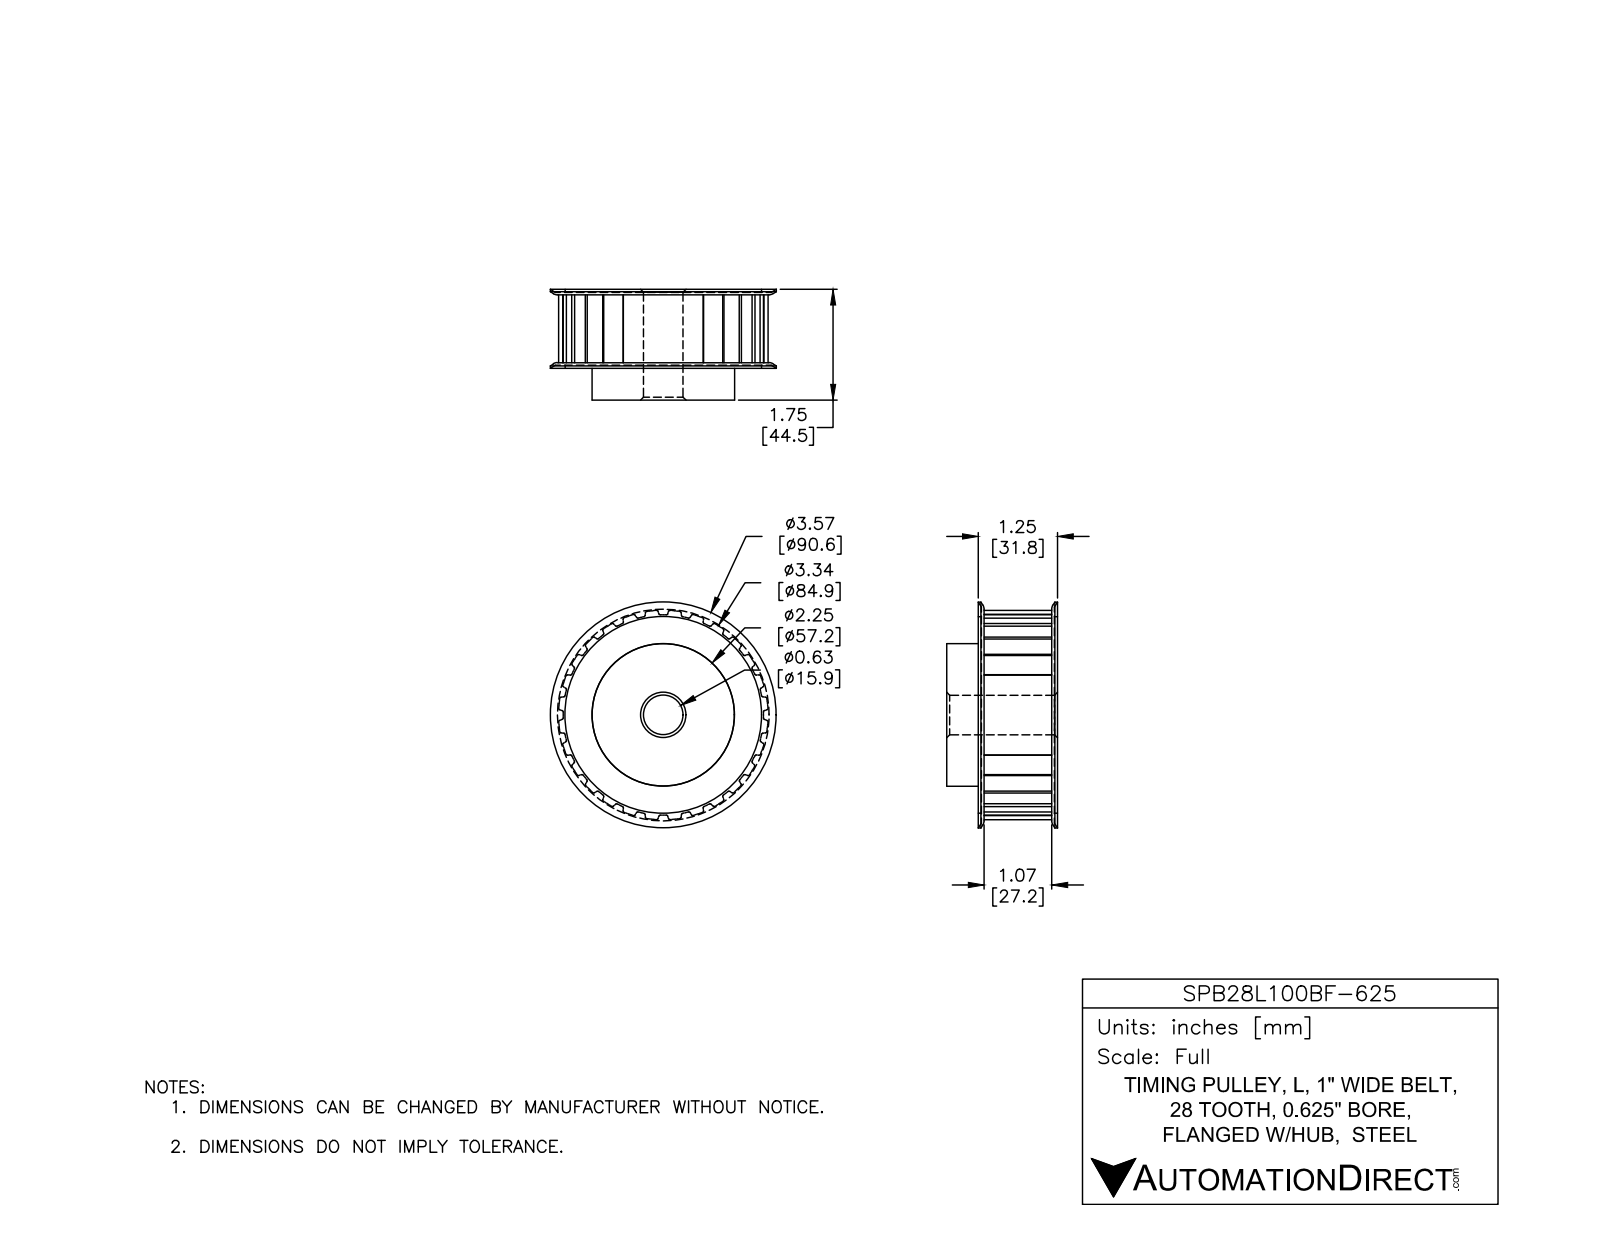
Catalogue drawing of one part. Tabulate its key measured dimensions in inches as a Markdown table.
| quantity | value |
| --- | --- |
| part name | SPB28L100BF-625 |
| STEP written by | SolidWorks 2015 (AUTOMOTIVE_DESIGN) |
| units | inches |
| bodies | 1 solid, 281 faces (91 planar, 174 cylindrical, 16 other) |
| overall size | 3.566 × 3.566 × 1.75 |
| volume | 11.87 in³ |
| surface area | 45.8 in² |
| round holes (diameter × count) | 0.625 × 1 |
| round bosses / shafts (diameter × count) | 3.566 × 1, 3.102 × 1, 2.25 × 1 |
| partial cylindrical surfaces (radius × count) | 0.02 × 112, 1.656 × 1 |
| main face-to-face distances | 1.25, 1.75, 0.5, 0.05, 1.2, 1.7, 1.15, 0.55, 0.09, 1.16 |
